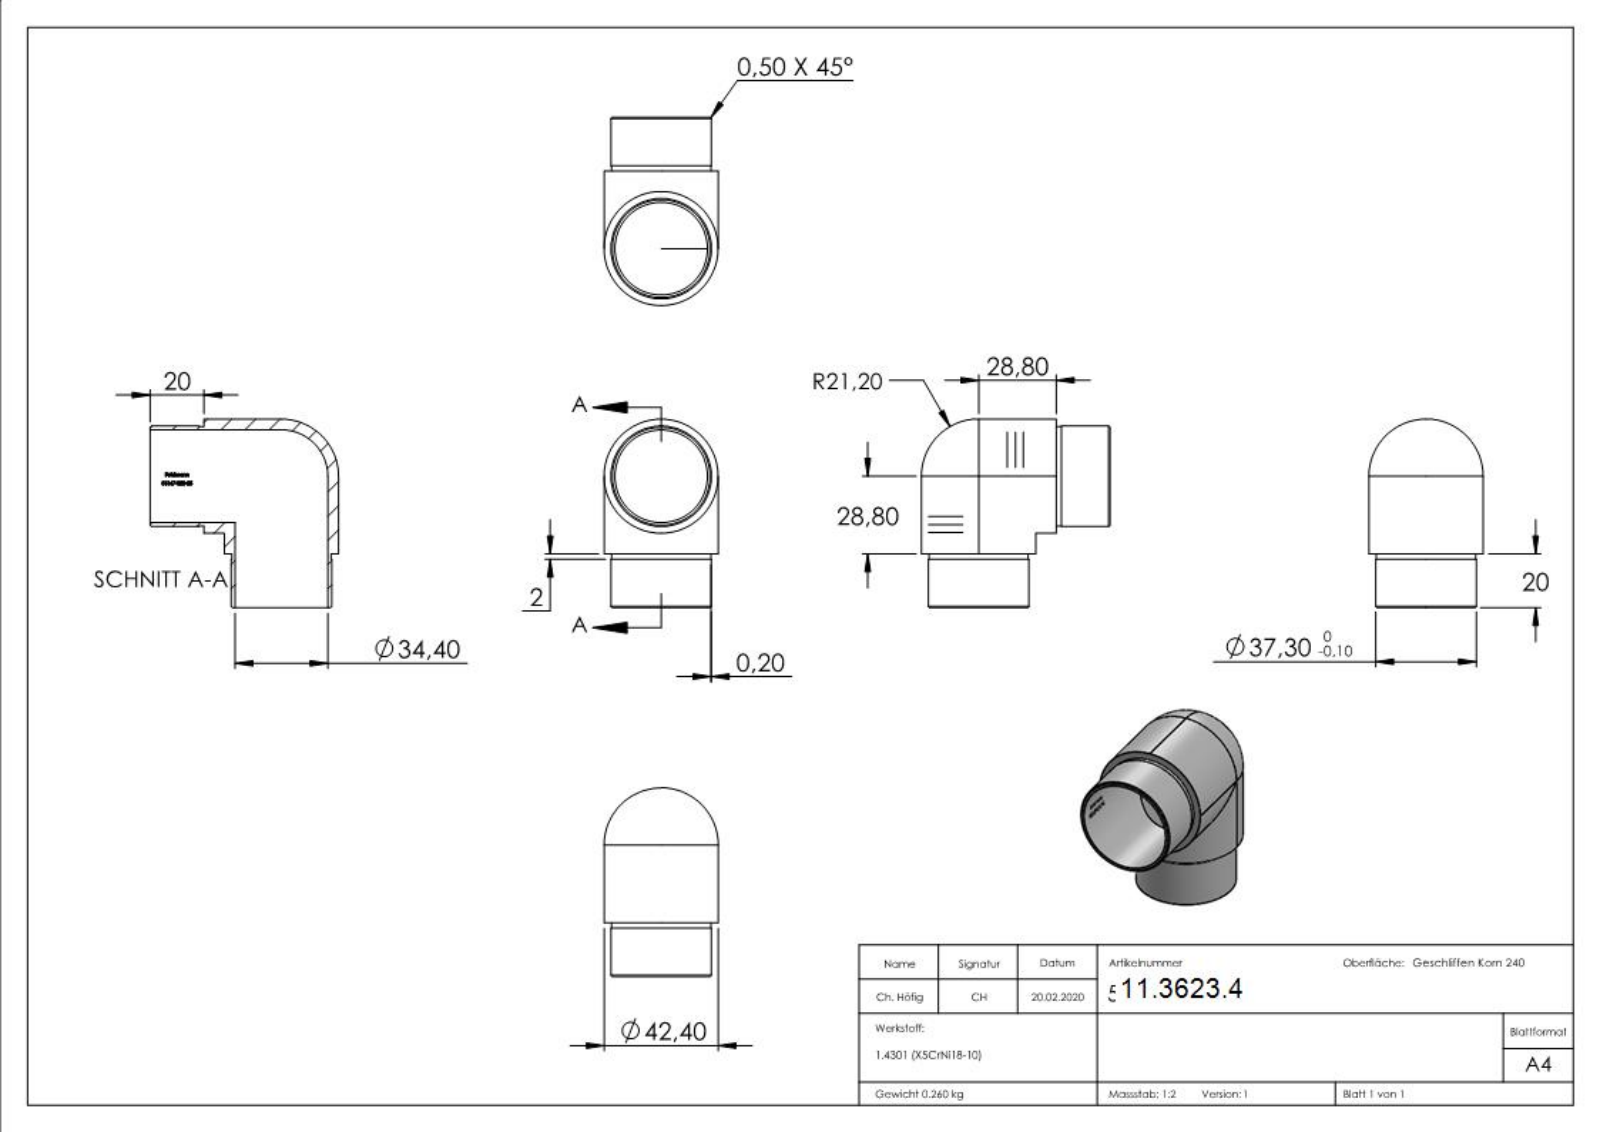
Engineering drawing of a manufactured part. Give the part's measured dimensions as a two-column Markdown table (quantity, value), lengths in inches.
| quantity | value |
| --- | --- |
| part name | 56167-320-25 |
| STEP written by | SolidWorks 2015 (CONFIG_CONTROL_DESIGN) |
| units | inches |
| bodies | 1 solid, 250 faces (94 planar, 38 cylindrical, 118 other) |
| overall size | 2.756 × 2.756 × 1.669 |
| volume | 2.01 in³ |
| surface area | 36.12 in² |
| round holes (diameter × count) | 1.354 × 2 |
| round bosses / shafts (diameter × count) | 1.669 × 2, 1.469 × 2, 1.453 × 2 |
| partial cylindrical surfaces (radius × count) | 0.697 × 1 |
| main face-to-face distances | 0.787, 0.709, 0.079, 0.015, 0.05, 0.117, 0.167, 0.052, 0.144, 0.129 |
